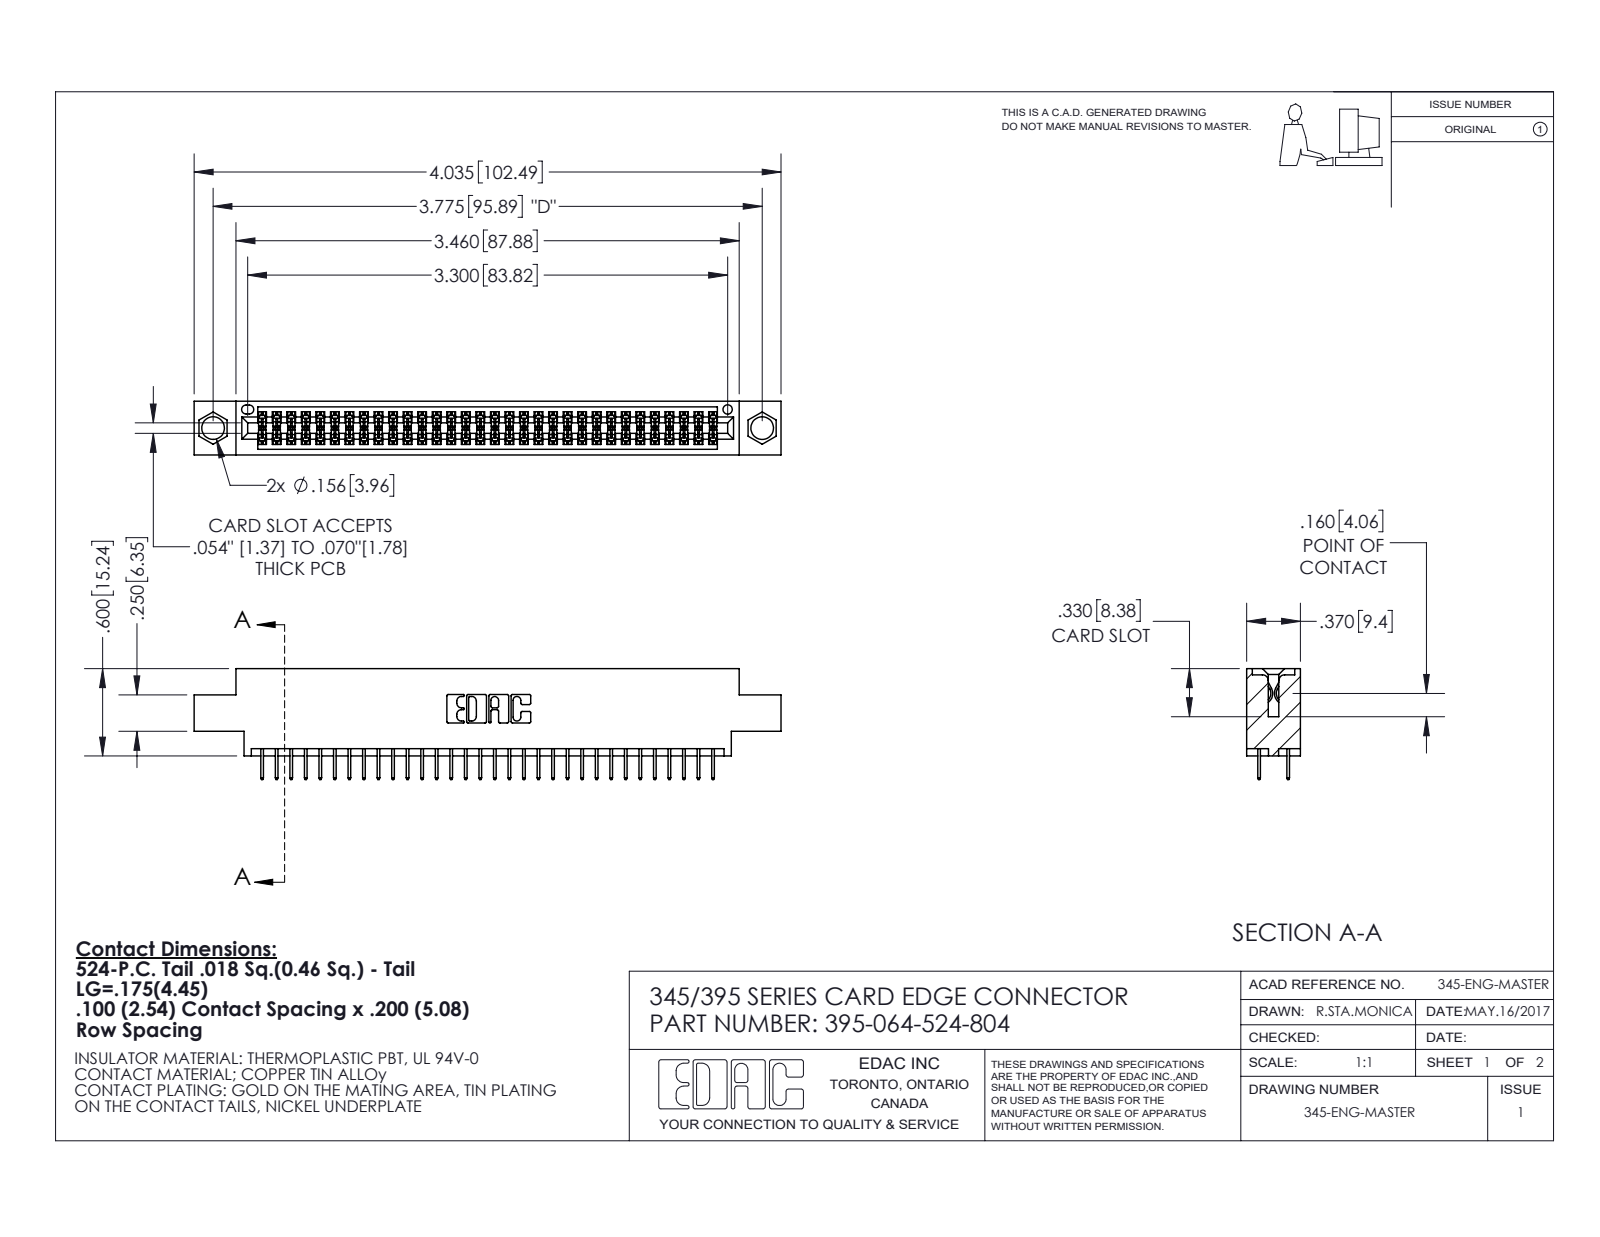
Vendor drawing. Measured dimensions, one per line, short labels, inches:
name: 345 Part_0.170 Offset - 0.156 Dia-TI; 345-292-001_345-293-124; 395-064-524-804
written by: SolidWorks 2020 (CONFIG_CONTROL_DESIGN)
unit: in
bodies: 65 solids, 3600 faces (2594 planar, 1006 cylindrical, 0 other)
size: 4.035 × 0.762 × 0.37
volume: 0.583 in³; area: 21.17 in²
holes: 2× ⌀0.156, 1× ⌀0.064
rounds: 96× R0.006, 22× R0.01, 6× R0.007, 6× R0.031, 3× R0.026, 2× R0.014, 2× R0.019, 2× R0.022
face distances: 0.072, 0.298, 0.37, 0.2, 0.098, 0.272, 0.025, 0.225, 0.175, 0.072
hole spacings: 0.27, 3.54, 3.775
